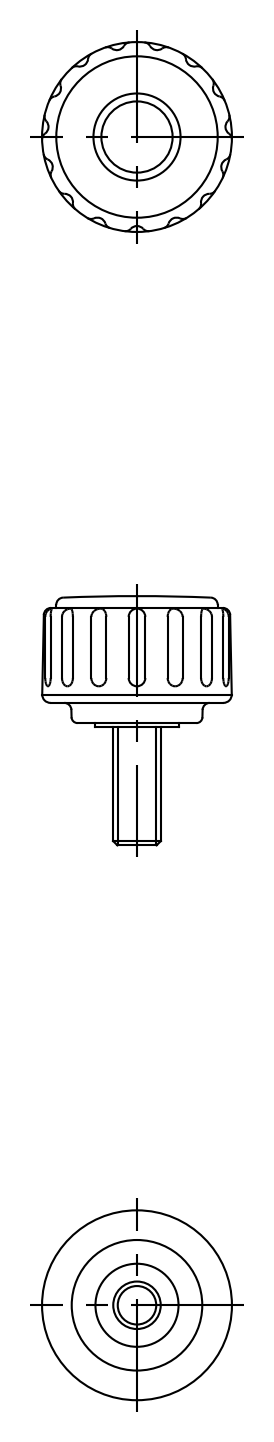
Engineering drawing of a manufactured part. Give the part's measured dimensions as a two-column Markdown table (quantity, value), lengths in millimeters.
| quantity | value |
| --- | --- |
| part name | screw; knob; KDMS_16_M4_10_WH_2951_36 |
| STEP written by | CADfix (AUTOMOTIVE_DESIGN) |
| units | millimeters |
| bodies | 2 solids, 68 faces (0 planar, 0 cylindrical, 68 other) |
| overall size | 20.95 × 16.12 × 15.97 |
| volume | 1 945 mm³ |
| surface area | 1 246 mm² |
